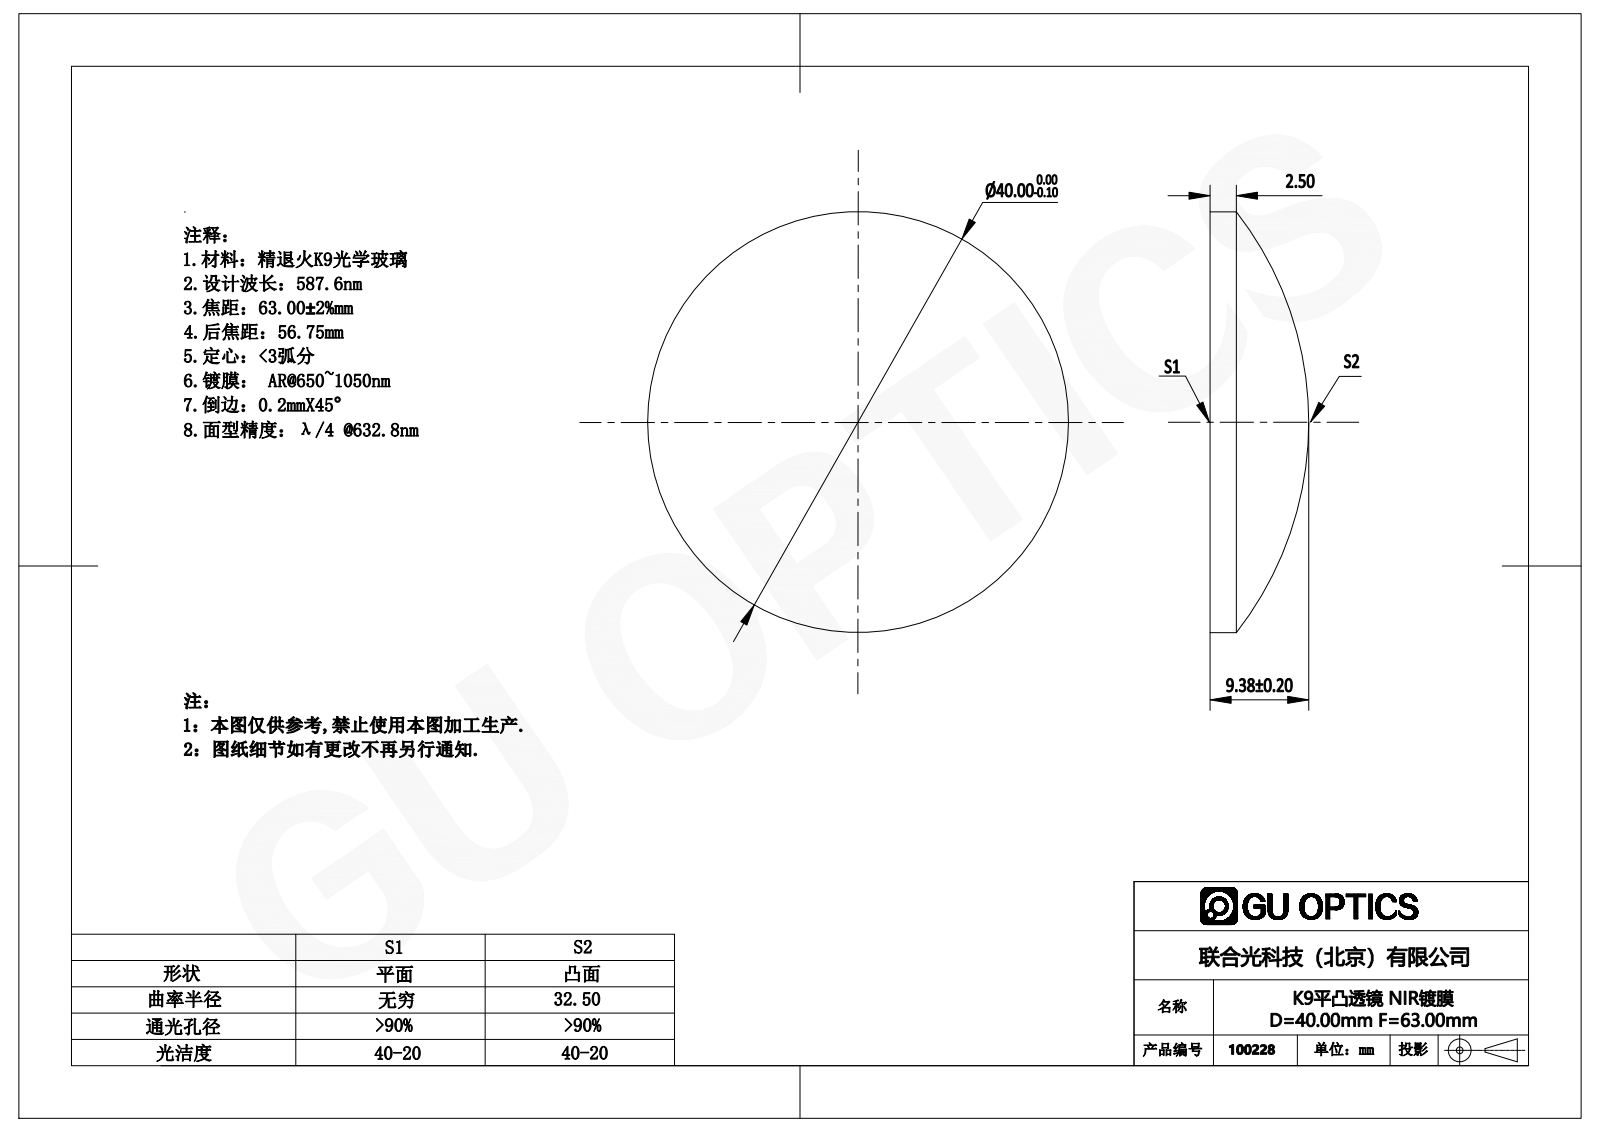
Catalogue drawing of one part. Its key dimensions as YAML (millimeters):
part_name: "100228"
step_written_by: "SolidWorks 2016 (AUTOMOTIVE_DESIGN)"
units: millimeters
bodies: {solids: 1, faces: 5, planar: 1, cylindrical: 2, other: 2}
overall_size: [40, 40, 9.38]
volume: 7635
surface_area: 2976
round_bosses_or_shafts:
  - {diameter: 40, count: 1}
